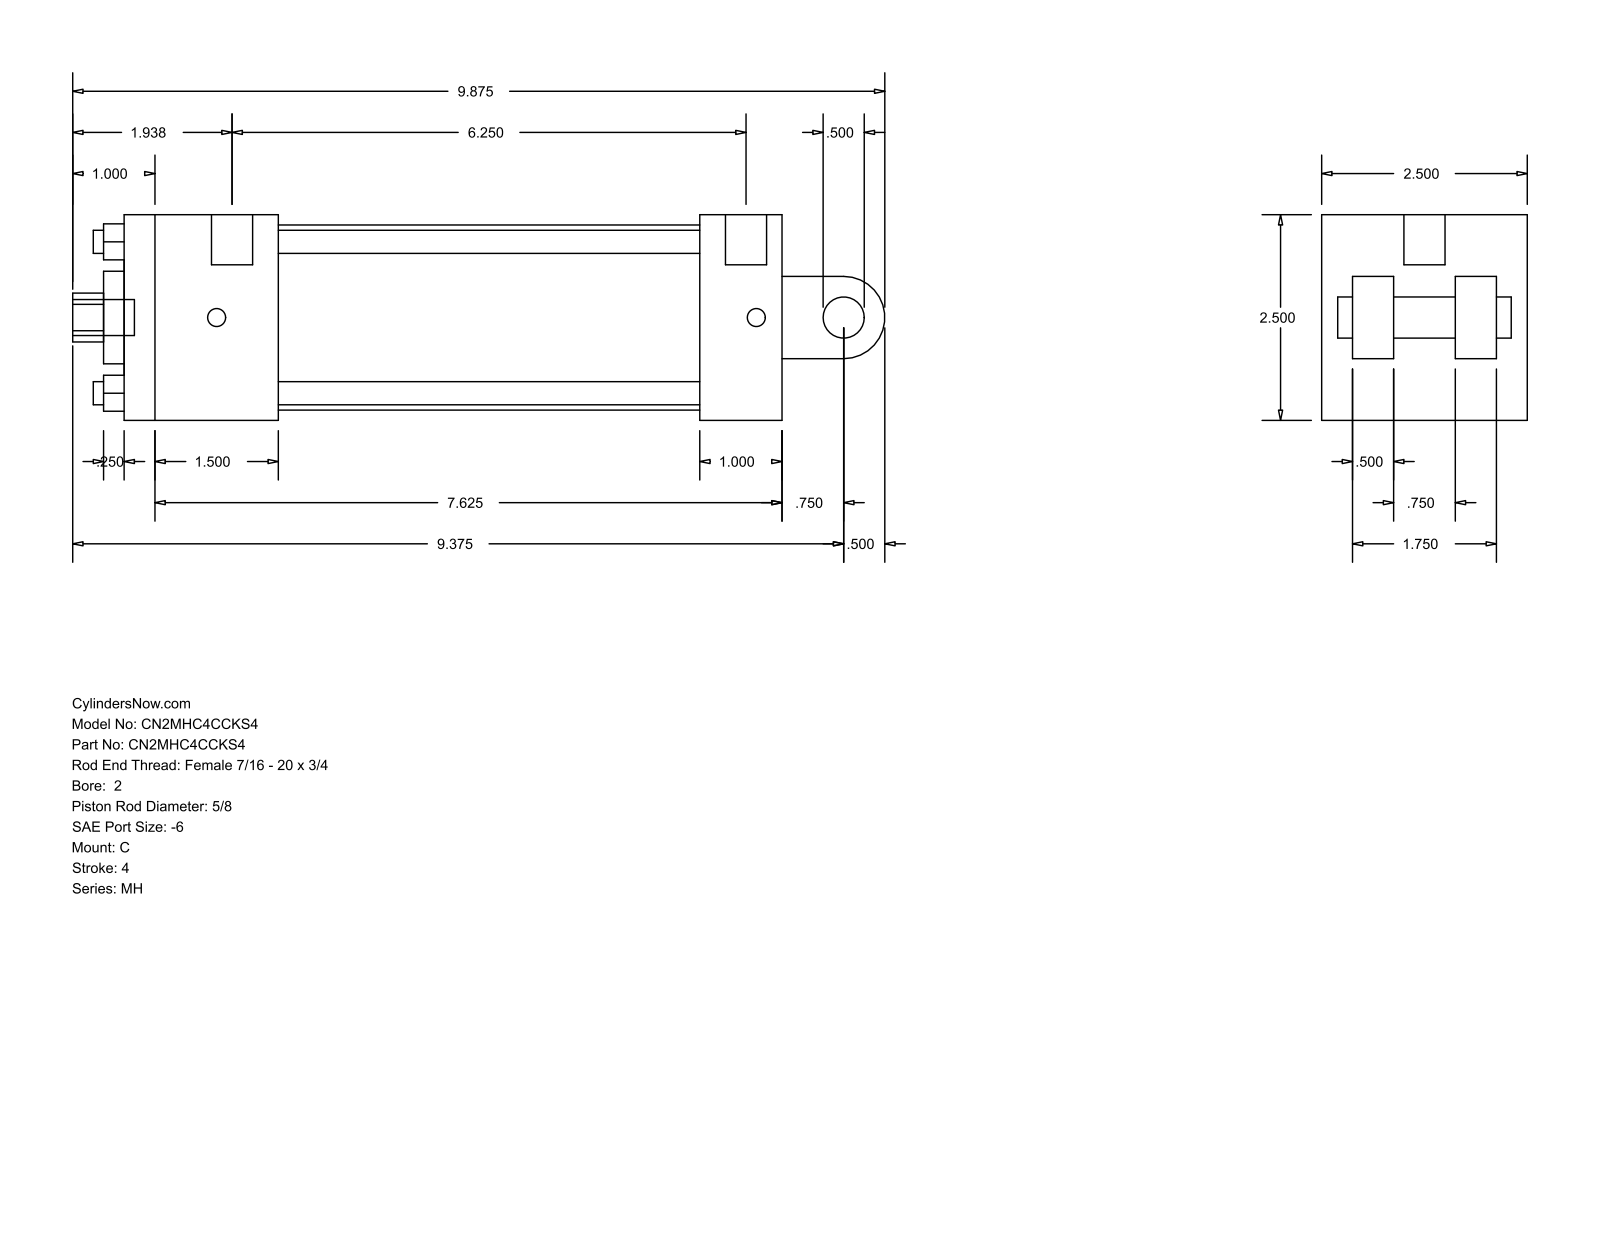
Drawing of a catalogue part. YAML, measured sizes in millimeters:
part_name: "MH_C__0200_0.625"
step_written_by: "GSSL Pune (CONFIG_CONTROL_DESIGN)"
units: millimeters
bodies: {solids: 0, faces: 99, planar: 70, cylindrical: 29, other: 0}
overall_size: [250.82, 63.5, 63.5]
round_holes:
  - {diameter: 7.14, count: 4}
  - {diameter: 5.56, count: 2}
  - {diameter: 12.7, count: 1}
  - {diameter: 15.88, count: 1}
  - {diameter: 28.57, count: 1}
  - {diameter: 57.15, count: 1}
round_bosses_or_shafts:
  - {diameter: 12.7, count: 2}
  - {diameter: 5.56, count: 2}
  - {diameter: 11.11, count: 1}
partial_cylinders:
  - {radius: 7.54, count: 1}
  - {radius: 12.7, count: 1}
face_to_face_distances: [63.5, 203.19, 12.7, 9.52, 47.62, 177.8, 130.18, 155.57, 25.39, 19.05]
hole_center_spacings: [33.05, 46.74, 66.1, 3.18]
